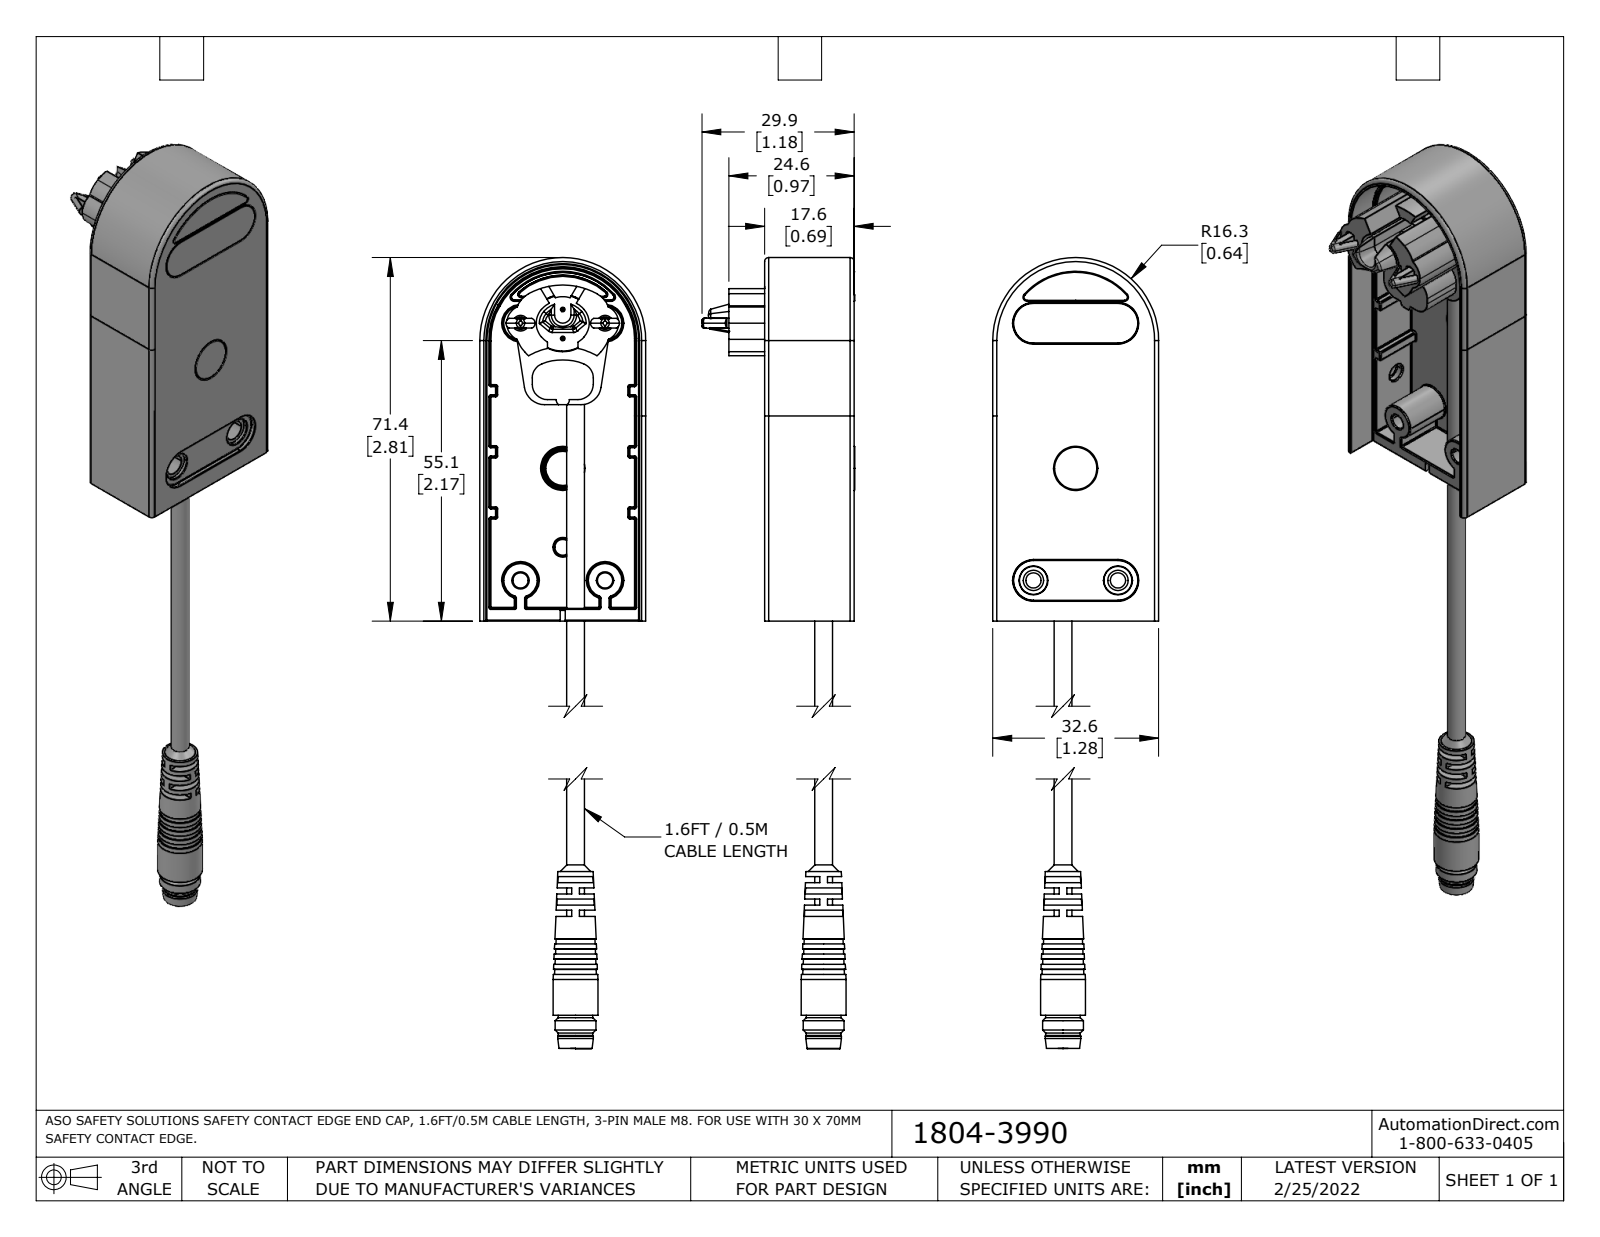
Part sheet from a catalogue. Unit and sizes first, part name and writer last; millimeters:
Units: millimetres
Overall size (bounding box): 172.2 × 32.6 × 30
Round holes (diameter × count): ⌀0.5 ×4, ⌀5.5 ×4, ⌀0.8 ×3, ⌀3.5 ×3, ⌀4 ×3, ⌀3 ×2, ⌀3.1 ×2, ⌀3.4 ×1, ⌀4 ×1, ⌀5.8 ×1
Round bosses / shafts (diameter × count): ⌀1.2 ×13, ⌀0.5 ×6, ⌀7 ×3, ⌀3.5 ×3, ⌀1 ×3, ⌀5 ×2, ⌀2.5 ×2, ⌀2 ×2
Partial cylindrical surfaces — rounded edges, fillets, slot ends (radius × count): R0.2 ×75, R0.1 ×17, R1 ×12, R0.3 ×6, R3 ×6, R3.5 ×6, R4 ×6, R0.5 ×5
Main face-to-face distances: 1.8, 2, 0.8, 32.6, 30.6, 1.2, 31.4, 29.4, 1, 28.6
Hole centre spacings: 16.6, 1.4, 8.73, 8.83, 10.54, 22.14, 22.66, 23.46
Volume: 17 606 mm³ · Surface area: 20 257 mm²
Bodies: 15 solids, 1027 faces (255 planar, 433 cylindrical, 339 other)
Part name (STEP PRODUCT): 1804-3990_Default
STEP written by: SolidWorks 2021 (CONFIG_CONTROL_DESIGN)
